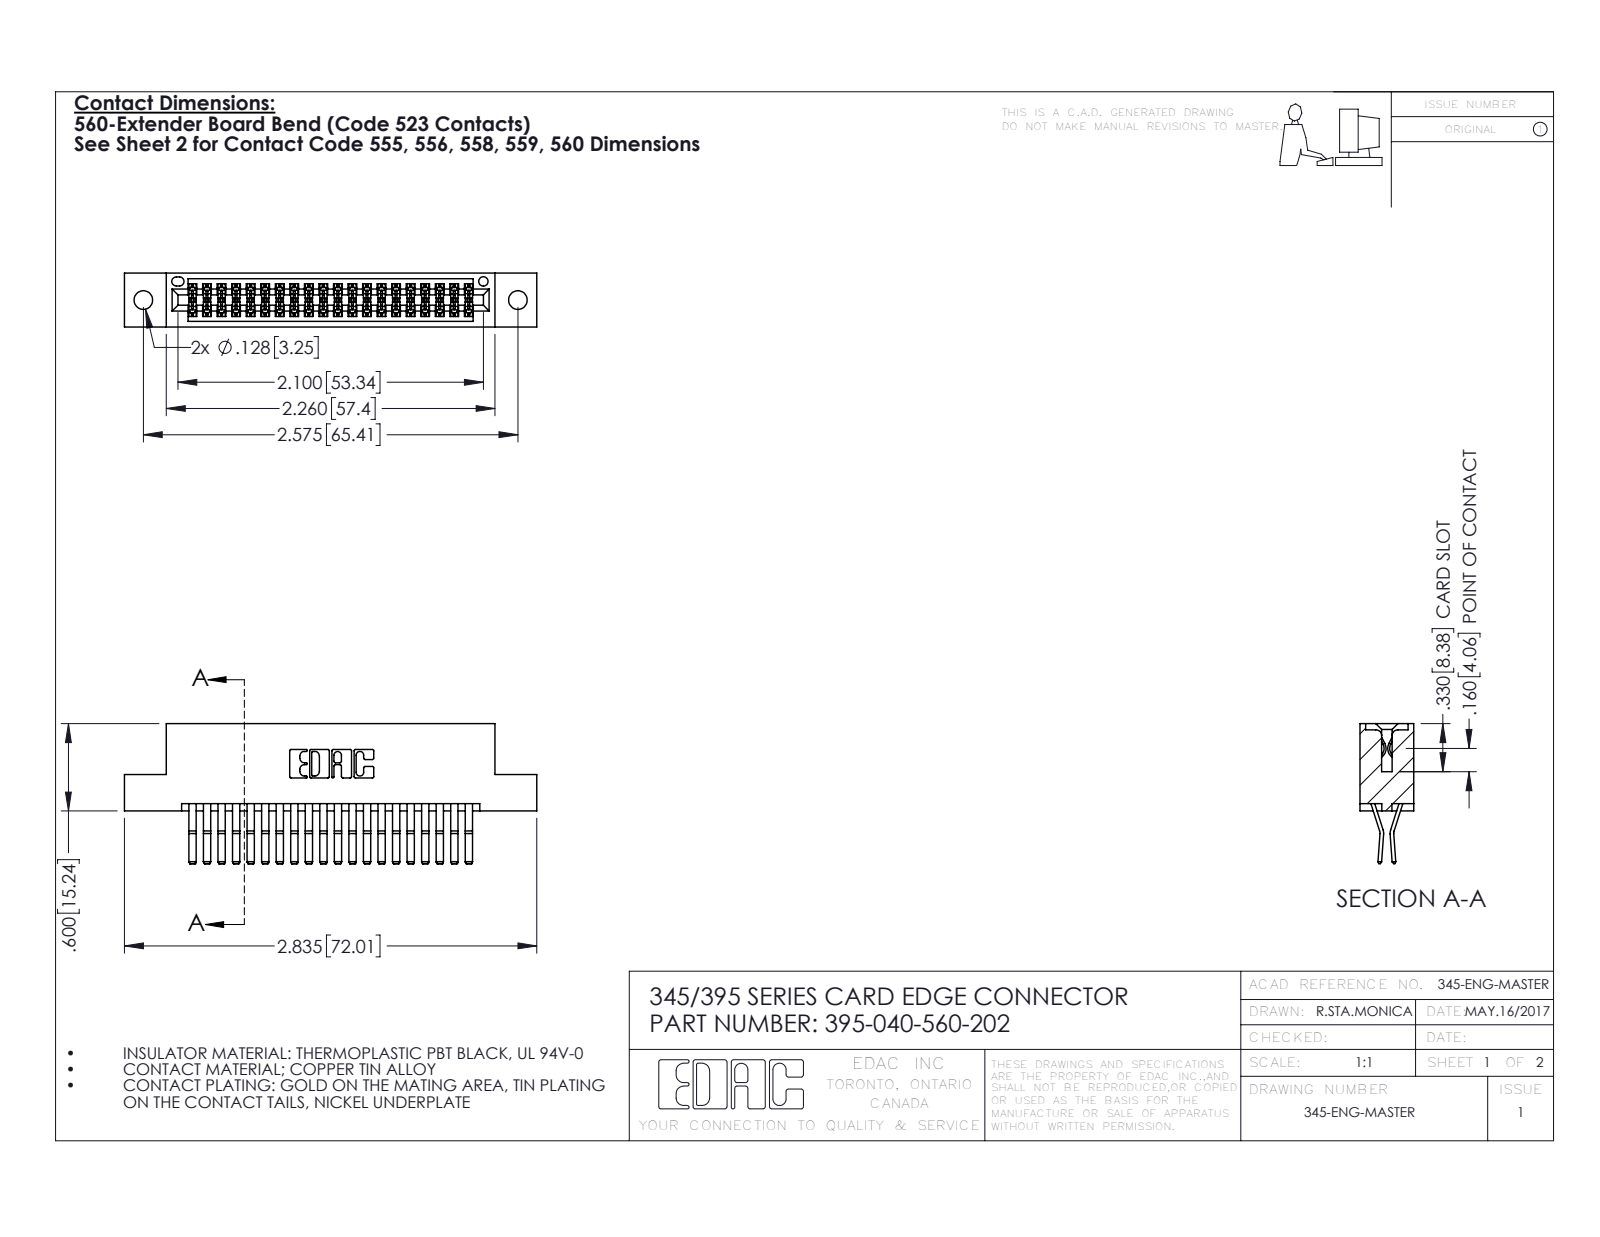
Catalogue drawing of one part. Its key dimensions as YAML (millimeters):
part_name: "395-040-560-202; 345-292-001_560 Tail; 345 Part_Flush Mounting Lugs - 0.128 Dia"
step_written_by: "SolidWorks 2016 (CONFIG_CONTROL_DESIGN)"
units: millimeters
bodies: {solids: 41, faces: 2206, planar: 1400, cylindrical: 806, other: 0}
overall_size: [72, 24.4, 9.4]
volume: 7010
surface_area: 10350
round_holes:
  - {diameter: 3.3, count: 2}
  - {diameter: 1.6, count: 1}
partial_cylinders:
  - {radius: 0.2, count: 60}
  - {radius: 0.3, count: 22}
  - {radius: 0.2, count: 6}
  - {radius: 0.8, count: 6}
  - {radius: 0.7, count: 3}
  - {radius: 0.3, count: 2}
  - {radius: 0.4, count: 2}
  - {radius: 0.5, count: 2}
face_to_face_distances: [0.6, 7.6, 1.8, 5.1, 9.4, 2.5, 6.9, 5.7, 4.4, 3.8]
hole_center_spacings: [6.9, 59.5, 65.4]
